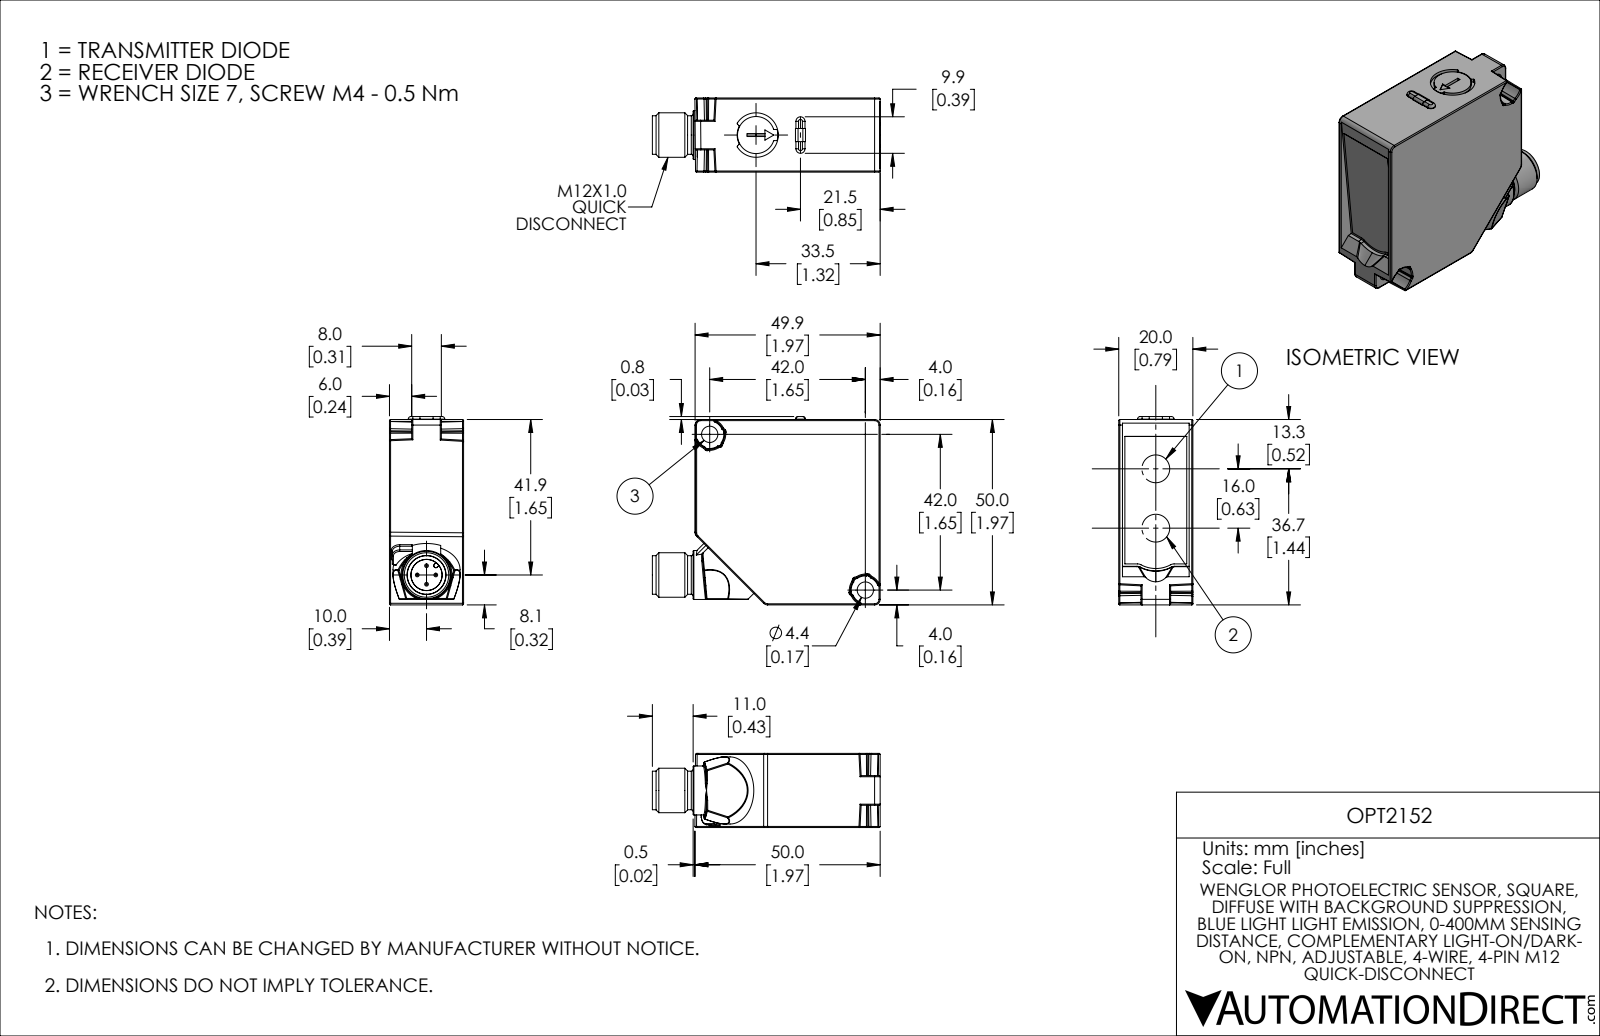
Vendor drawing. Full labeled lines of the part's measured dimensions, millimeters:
Part name (STEP PRODUCT): OPT2151_52
STEP written by: SolidWorks 2019 (AUTOMOTIVE_DESIGN)
Units: millimetres
Bodies: 3 solids, 350 faces (113 planar, 122 cylindrical, 115 other)
Overall size (bounding box): 70.5 × 50.8 × 20
Volume: 46 150 mm³ · Surface area: 10 100 mm²
Round holes (diameter × count): ⌀4.4 ×2, ⌀12 ×1, ⌀18.1 ×1
Round bosses / shafts (diameter × count): ⌀1 ×4, ⌀0.2 ×2, ⌀13.2 ×1, ⌀12 ×1, ⌀10.4 ×1, ⌀10 ×1
Partial cylindrical surfaces — rounded edges, fillets, slot ends (radius × count): R0.3 ×64, R0.2 ×8, R1.5 ×5, R2 ×5, R0.7 ×4, R1.2 ×2, R5.1 ×1, R5.9 ×1
Main face-to-face distances: 20, 50, 1, 19, 6, 14, 5, 13, 1.5, 48.5
Hole centre spacings: 59.4
